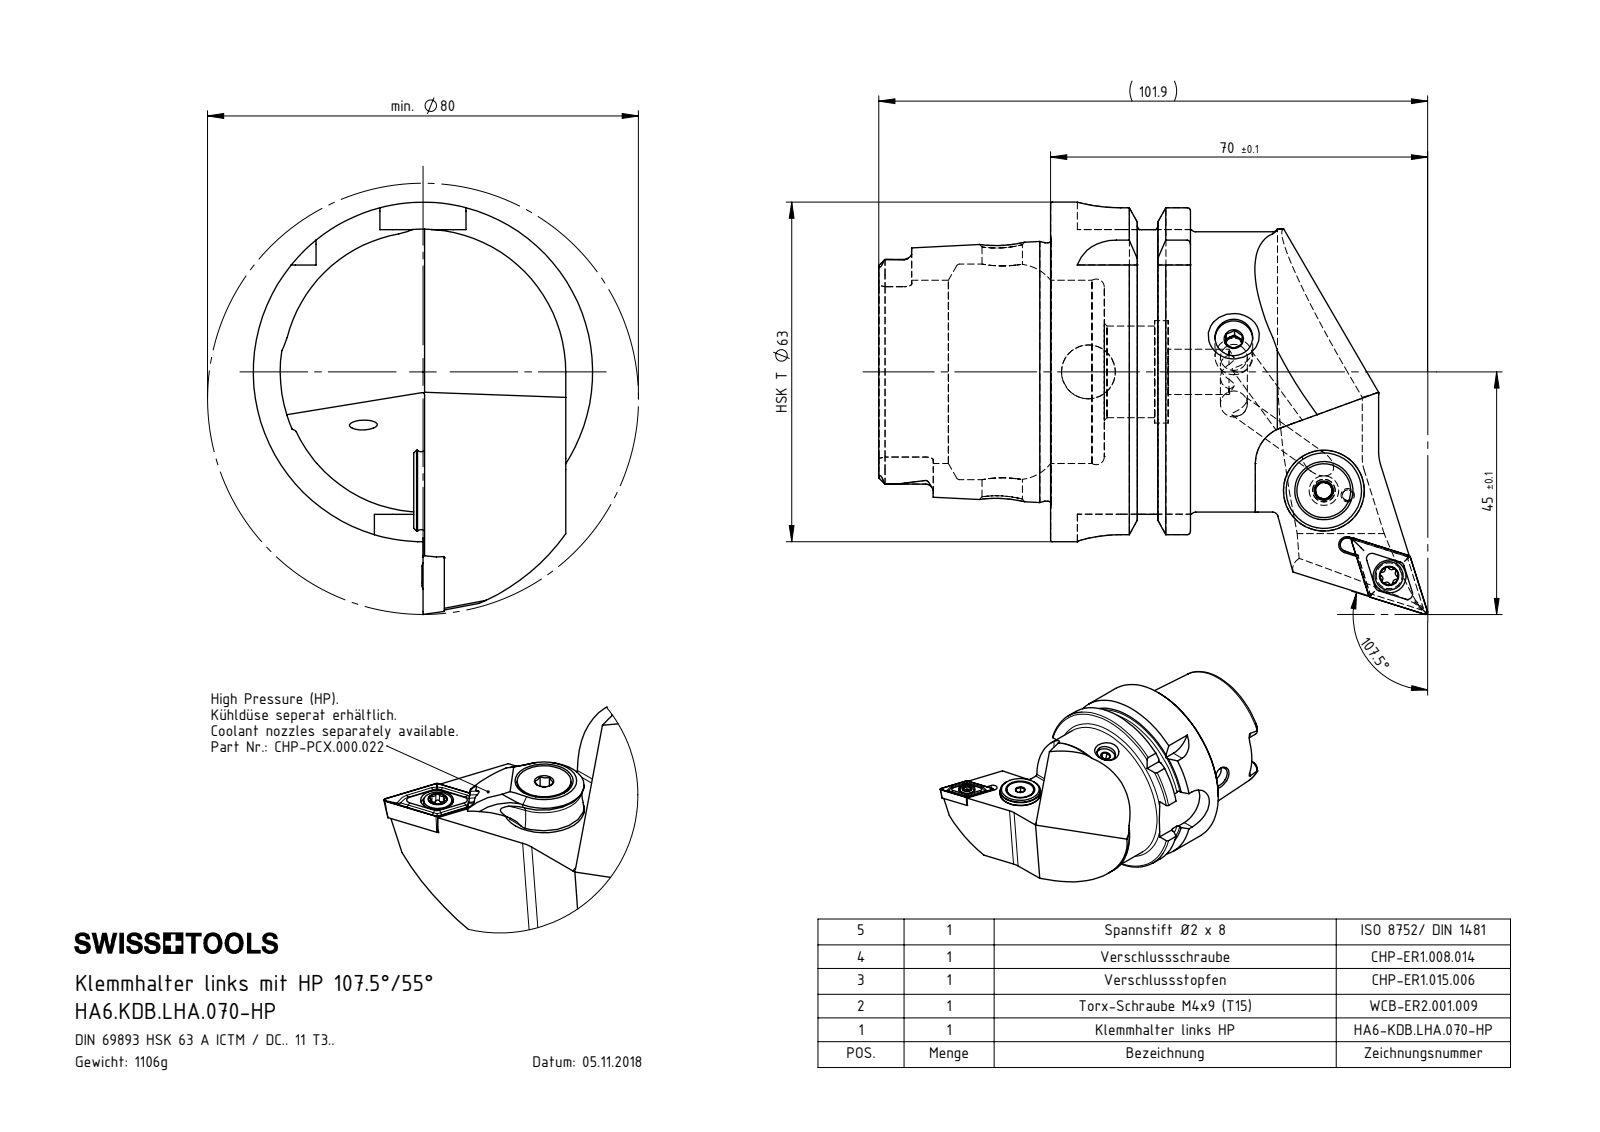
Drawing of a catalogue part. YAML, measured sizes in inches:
part_name: "DIN 3771 - 13x1; ISO 8752 2x8; CHP-ER1.008.014_A; HA6.KDB.LHA.070-HP (+7 more)"
step_written_by: "SolidWorks 2017 (AUTOMOTIVE_DESIGN)"
units: inches
bodies: {solids: 9, faces: 518, planar: 131, cylindrical: 153, other: 234}
overall_size: [4.012, 3.012, 2.48]
volume: 8.607
surface_area: 51.81
round_holes:
  - {diameter: 0.165, count: 2}
  - {diameter: 0.197, count: 2}
  - {diameter: 0.047, count: 1}
  - {diameter: 0.079, count: 1}
  - {diameter: 0.118, count: 1}
  - {diameter: 0.13, count: 1}
  - {diameter: 0.173, count: 1}
  - {diameter: 0.209, count: 1}
  - {diameter: 0.24, count: 1}
  - {diameter: 0.276, count: 1}
  - {diameter: 0.295, count: 1}
  - {diameter: 0.331, count: 1}
round_bosses_or_shafts:
  - {diameter: 2.48, count: 1}
  - {diameter: 2.163, count: 1}
  - {diameter: 2.047, count: 1}
  - {diameter: 1.887, count: 1}
  - {diameter: 0.585, count: 1}
  - {diameter: 0.528, count: 1}
  - {diameter: 0.394, count: 1}
  - {diameter: 0.315, count: 1}
partial_cylinders:
  - {radius: 0.039, count: 7}
  - {radius: 0.013, count: 6}
  - {radius: 0.023, count: 6}
  - {radius: 0.055, count: 6}
  - {radius: 0.02, count: 4}
  - {radius: 0.315, count: 4}
  - {radius: 0.236, count: 3}
  - {radius: 0.043, count: 2}
face_to_face_distances: [1.022, 0.63, 0.392, 1.031, 1.256, 1.648, 2.278, 2.079, 0.858, 0.467]
hole_center_spacings: [0.177, 0.662, 0.667, 0.784, 0.789, 1.927, 2.098, 2.655]
